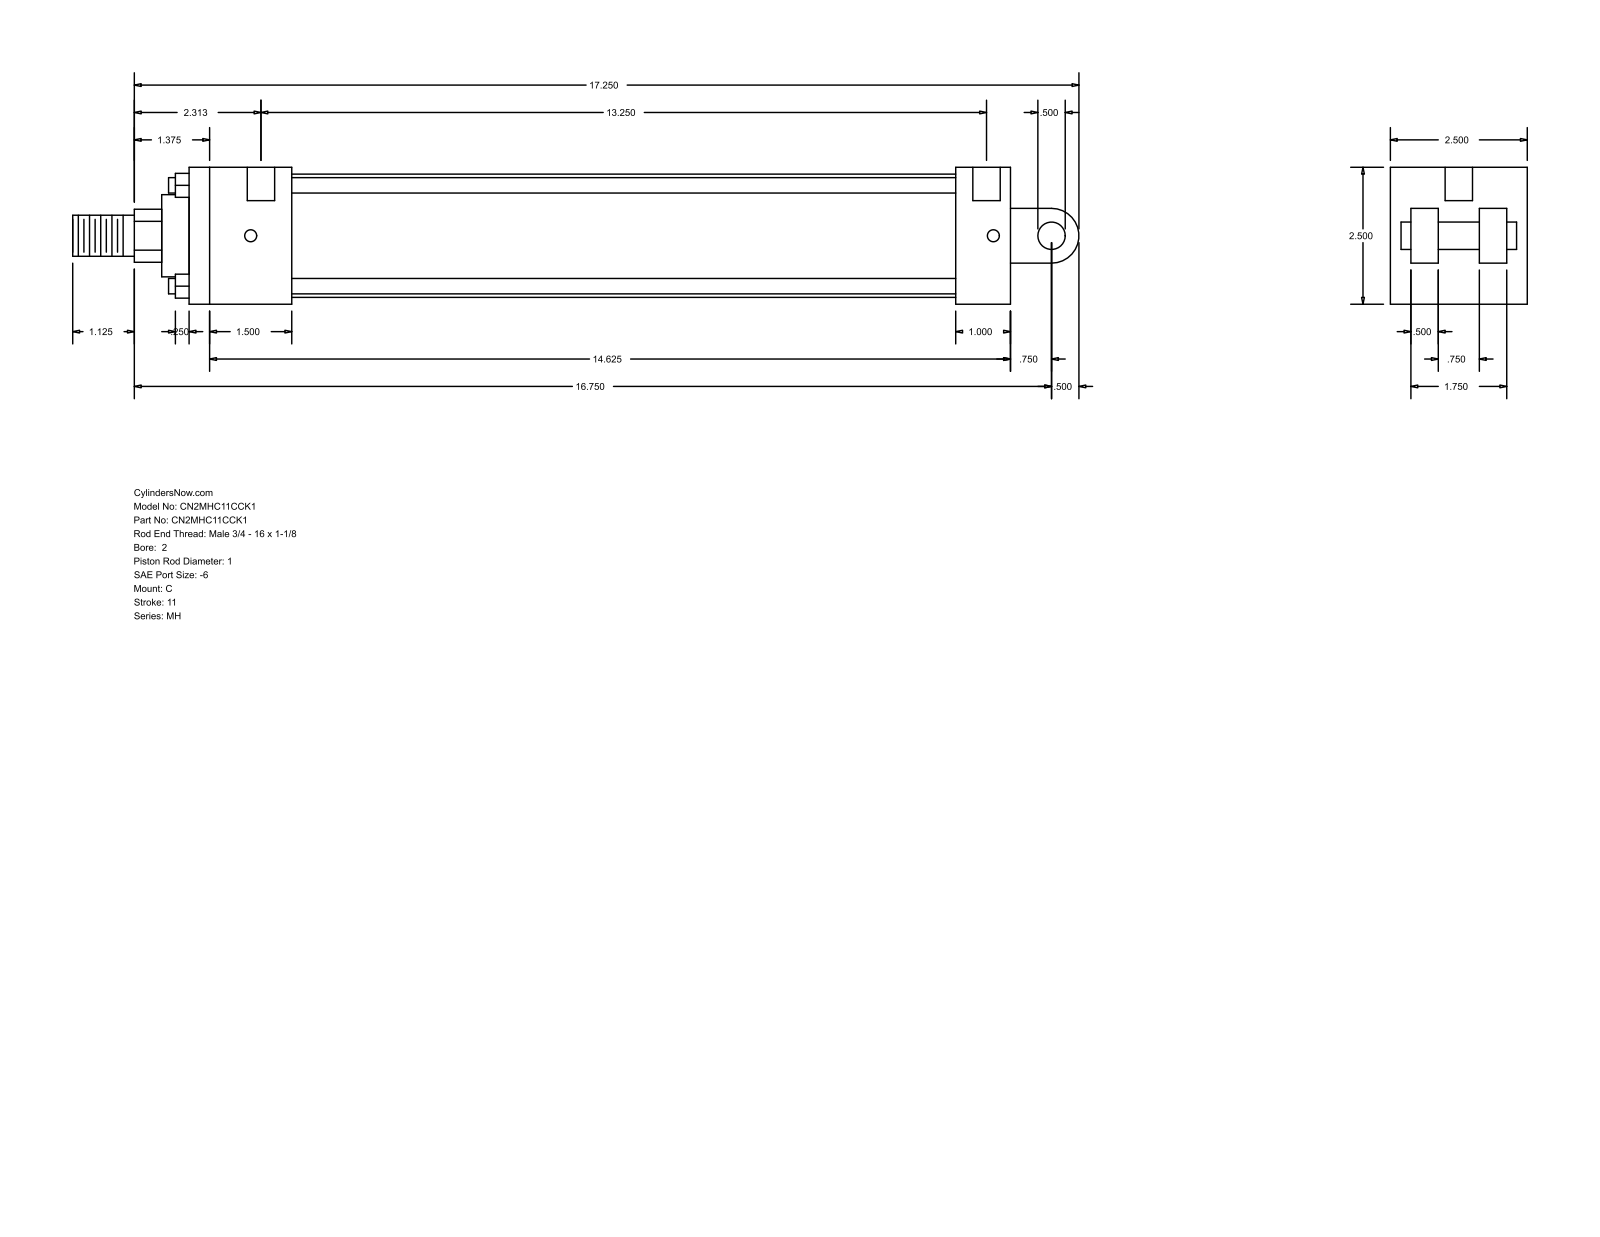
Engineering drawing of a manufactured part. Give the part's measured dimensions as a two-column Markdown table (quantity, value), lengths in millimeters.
| quantity | value |
| --- | --- |
| part name | MH_C__0200_1 |
| STEP written by | GSSL Pune (CONFIG_CONTROL_DESIGN) |
| units | millimeters |
| bodies | 0 solids, 99 faces (70 planar, 29 cylindrical, 0 other) |
| overall size | 466.73 × 63.5 × 63.5 |
| round holes (diameter × count) | 5.56 × 4, 12.7 × 2 |
| round bosses / shafts (diameter × count) | 7.14 × 4, 57.15 × 1, 38.1 × 1, 25.4 × 1, 19.05 × 1, 12.7 × 1 |
| partial cylindrical surfaces (radius × count) | 12.29 × 1, 12.7 × 1 |
| main face-to-face distances | 63.5, 381, 12.7, 25.4, 47.63, 53.98, 9.52, 355.6, 307.97, 333.37 |
| hole center spacings | 344.48, 3.17, 4.76, 336.55, 339.72, 341.31 |
